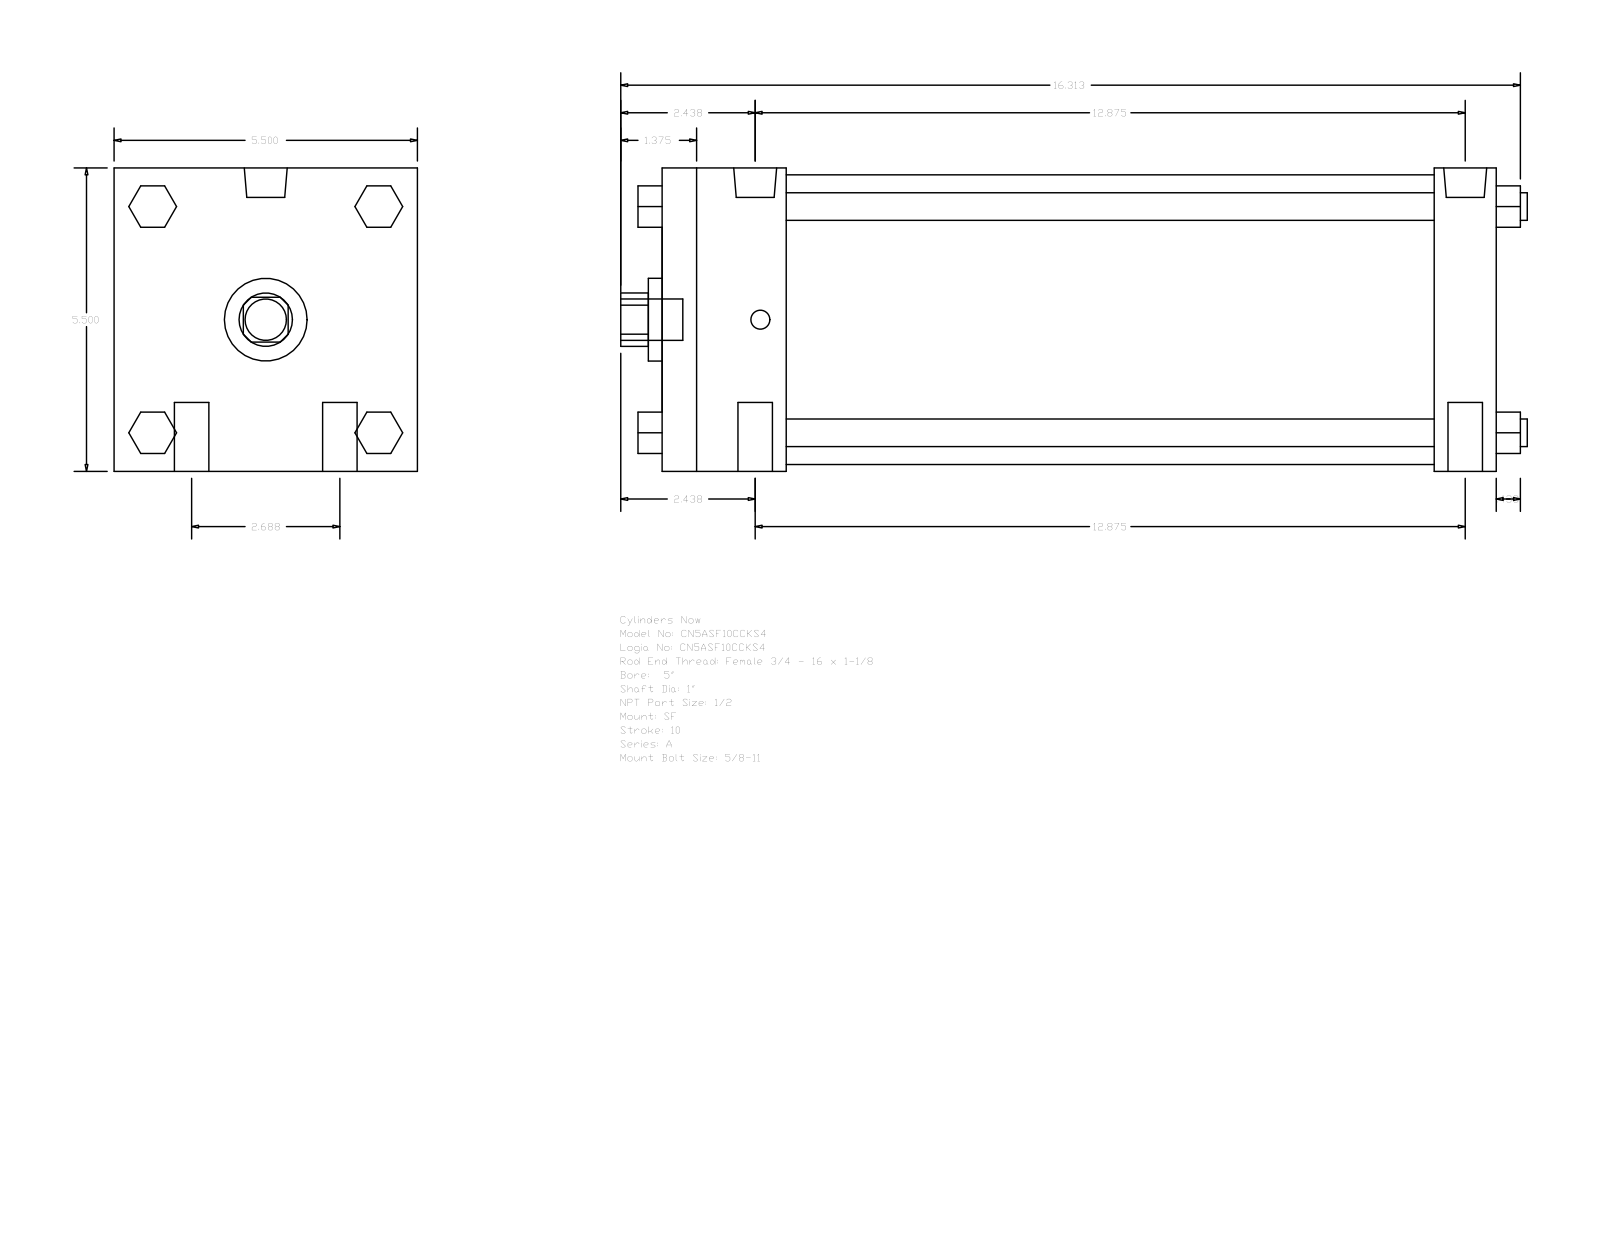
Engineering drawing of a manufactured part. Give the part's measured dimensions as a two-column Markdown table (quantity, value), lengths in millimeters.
| quantity | value |
| --- | --- |
| part name | A_SF__0500_1 |
| STEP written by | GSSL Pune (CONFIG_CONTROL_DESIGN) |
| units | millimeters |
| bodies | 0 solids, 124 faces (94 planar, 30 cylindrical, 0 other) |
| overall size | 417.51 × 139.7 × 139.7 |
| round holes (diameter × count) | 25.4 × 1, 38.1 × 1, 133.35 × 1 |
| round bosses / shafts (diameter × count) | 15.88 × 4, 12.7 × 4, 19.77 × 2, 8.73 × 2, 19.05 × 1 |
| partial cylindrical surfaces (radius × count) | 12.29 × 1 |
| main face-to-face distances | 139.7, 384.18, 57.15, 355.6, 298.45, 327.03, 28.58, 19.05, 52.07, 90.18 |
